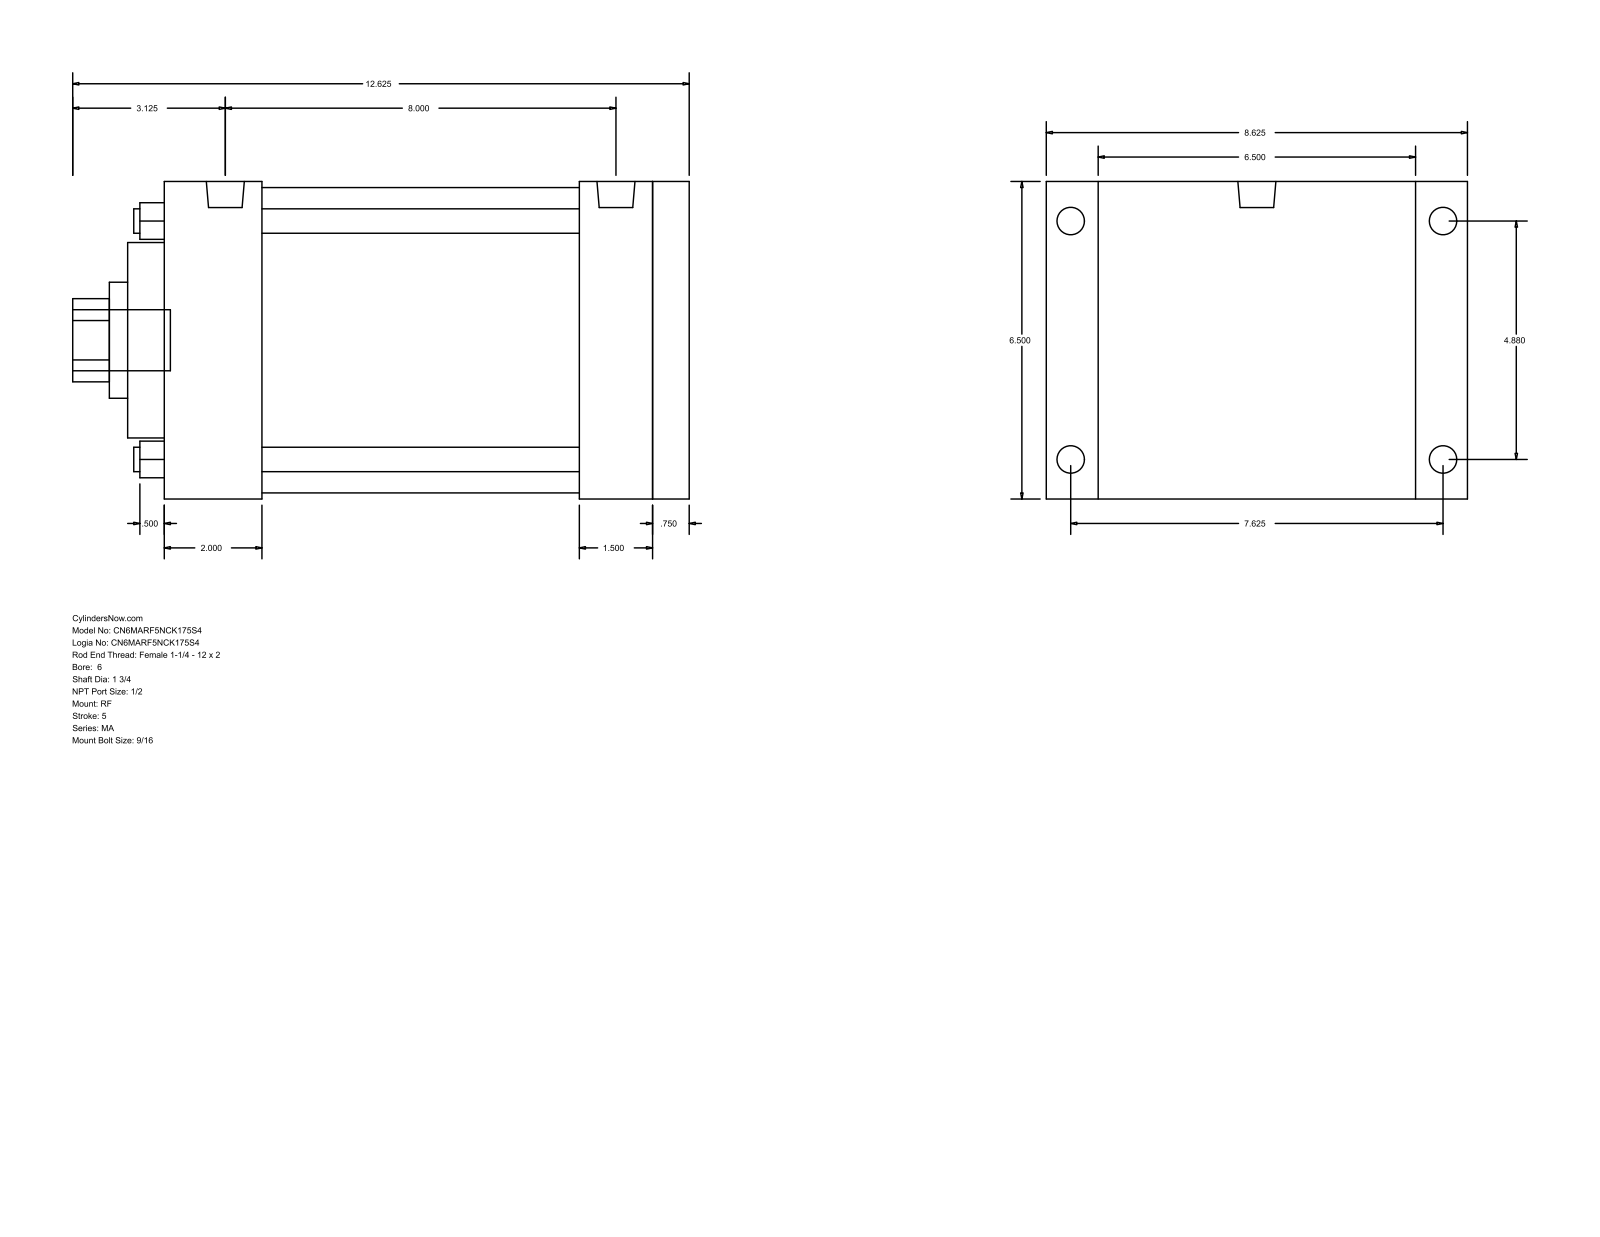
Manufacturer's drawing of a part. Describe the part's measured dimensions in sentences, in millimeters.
The part is named "MA_RF__0600_1.75". Its 3-D file was written by "GSSL Pune (CONFIG_CONTROL_DESIGN)". It is 0 solids with 94 faces: 65 planar, 29 cylindrical and 0 other. Overall it measures 320.68 by 219.07 by 165.1 millimeters. Round holes: 4 of diameter 12.7, 1 of diameter 44.45, 1 of diameter 60.33, 1 of diameter 101.6, 1 of diameter 158.75. Round bosses or shafts: 4 of diameter 17.46, 4 of diameter 14.29, 2 of diameter 19.77, 1 of diameter 31.75. Partial cylindrical surfaces (rounded edges, fillets, slot ends): 1 of radius 21.63. The main face-to-face distances are 165.1, 273.06, 254, 19.06, 19.05, 38.1, 50.8, 203.2, 222.26, 215.9. The hole center spacings are 87.65, 123.96, 175.31.
